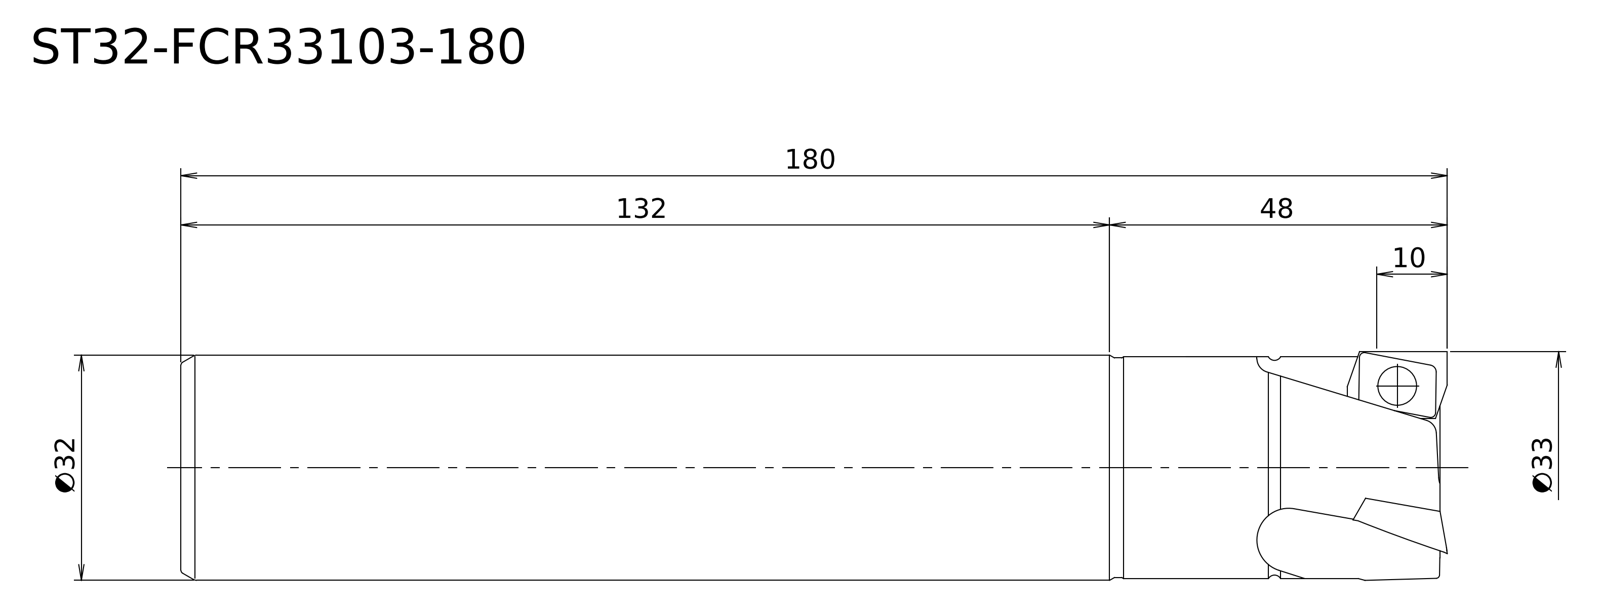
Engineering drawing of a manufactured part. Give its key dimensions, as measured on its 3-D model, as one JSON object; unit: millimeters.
{"step_written_by": "Kubotek KeyCreator V8.5.1 (14335) (CONFIG_CONTROL_DESIGN)", "units": "millimeters", "bodies": {"solids": 1, "faces": 7, "planar": 2, "cylindrical": 3, "other": 2}, "overall_size": [180, 33, 33], "volume_mm3": 144530, "surface_area_mm2": 19800, "round_bosses_or_shafts": [[33, 1], [32, 1], [31.5, 1]], "face_to_face_distances": [180]}
